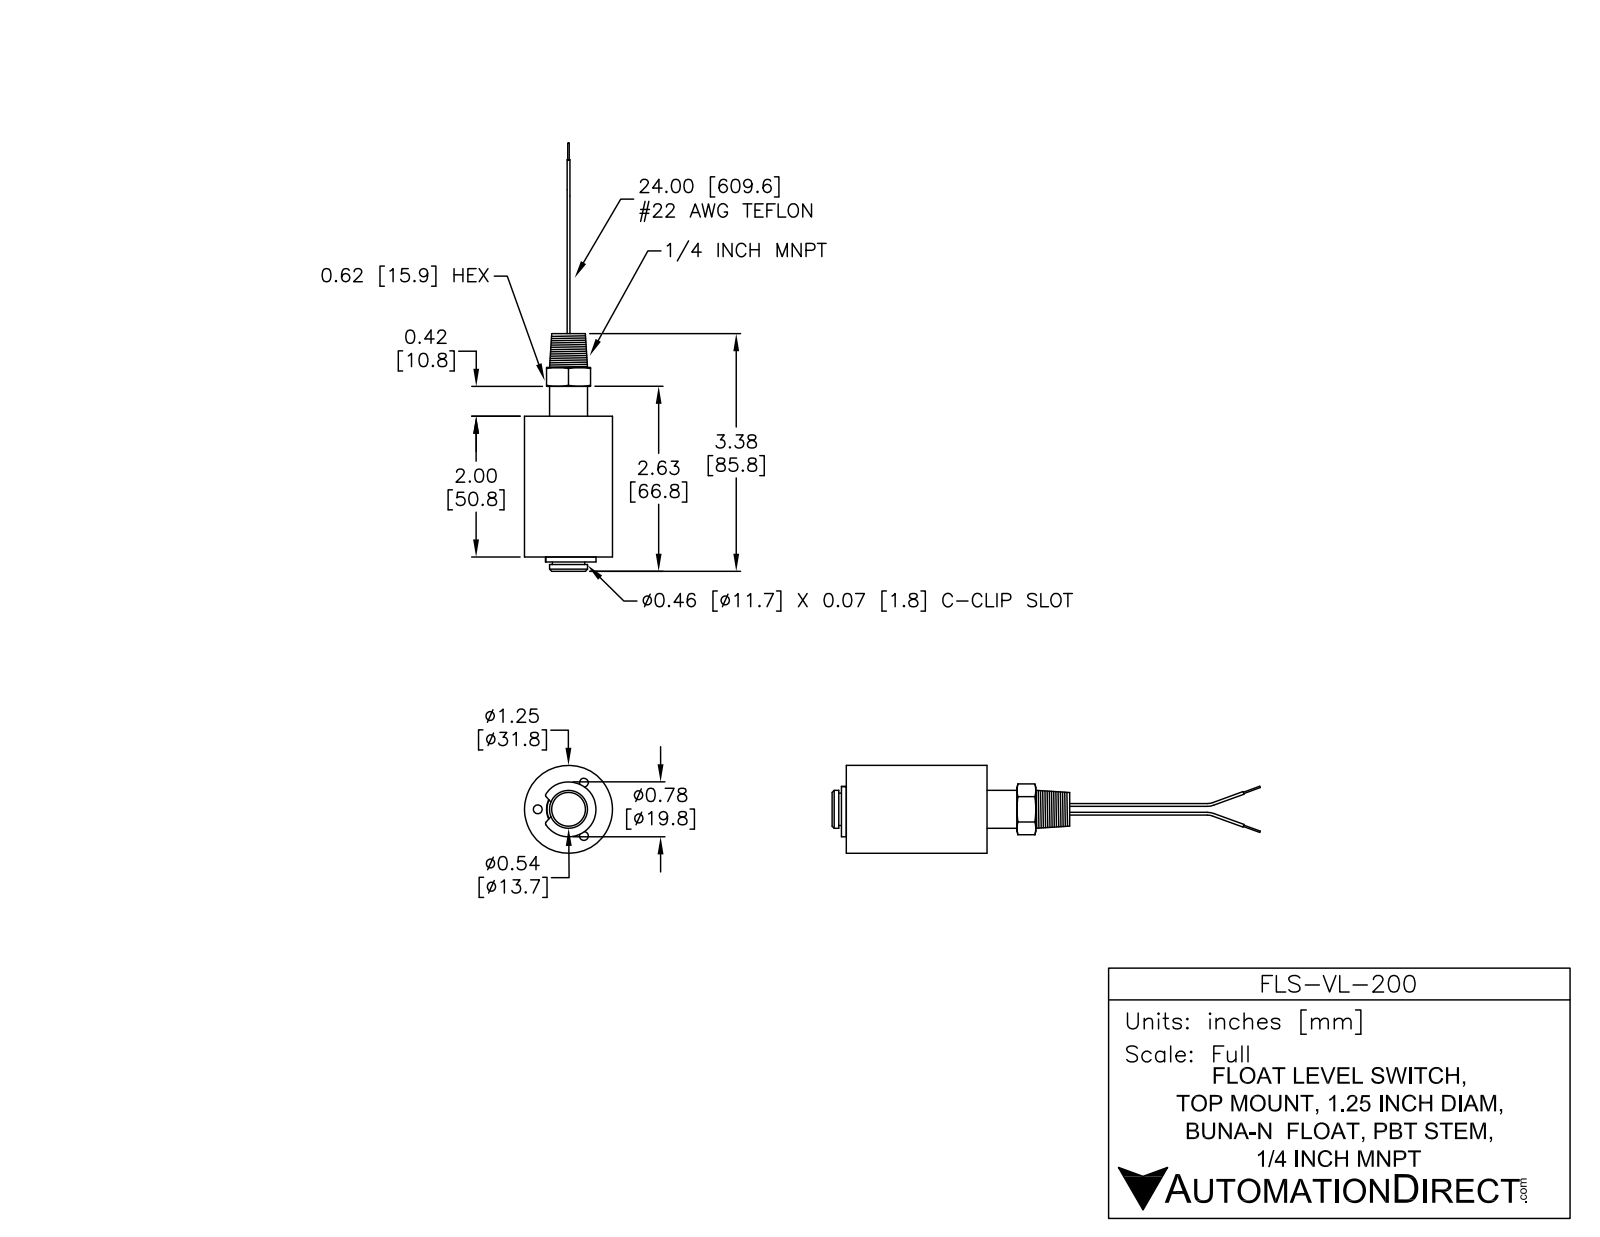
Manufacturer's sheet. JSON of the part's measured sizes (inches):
{"part_name": "FLS-VL-200", "step_written_by": "SolidWorks 2013 (AUTOMOTIVE_DESIGN)", "units": "inches", "bodies": {"solids": 5, "faces": 68, "planar": 25, "cylindrical": 35, "other": 8}, "overall_size": [6.099, 1.25, 1.25], "volume_in3": 2.136, "surface_area_in2": 25.77, "round_holes": [[0.45, 1], [0.46, 1], [0.63, 1]], "round_bosses_or_shafts": [[0.04, 4], [0.02, 2], [1.25, 1], [0.78, 1], [0.54, 1]], "partial_cylinders_radius": [[0.031, 4]], "face_to_face_distances": [1.92, 0.168, 2.087, 0.161, 2.081, 0.076, 0.07, 0.091, 2.011, 0.625]}
